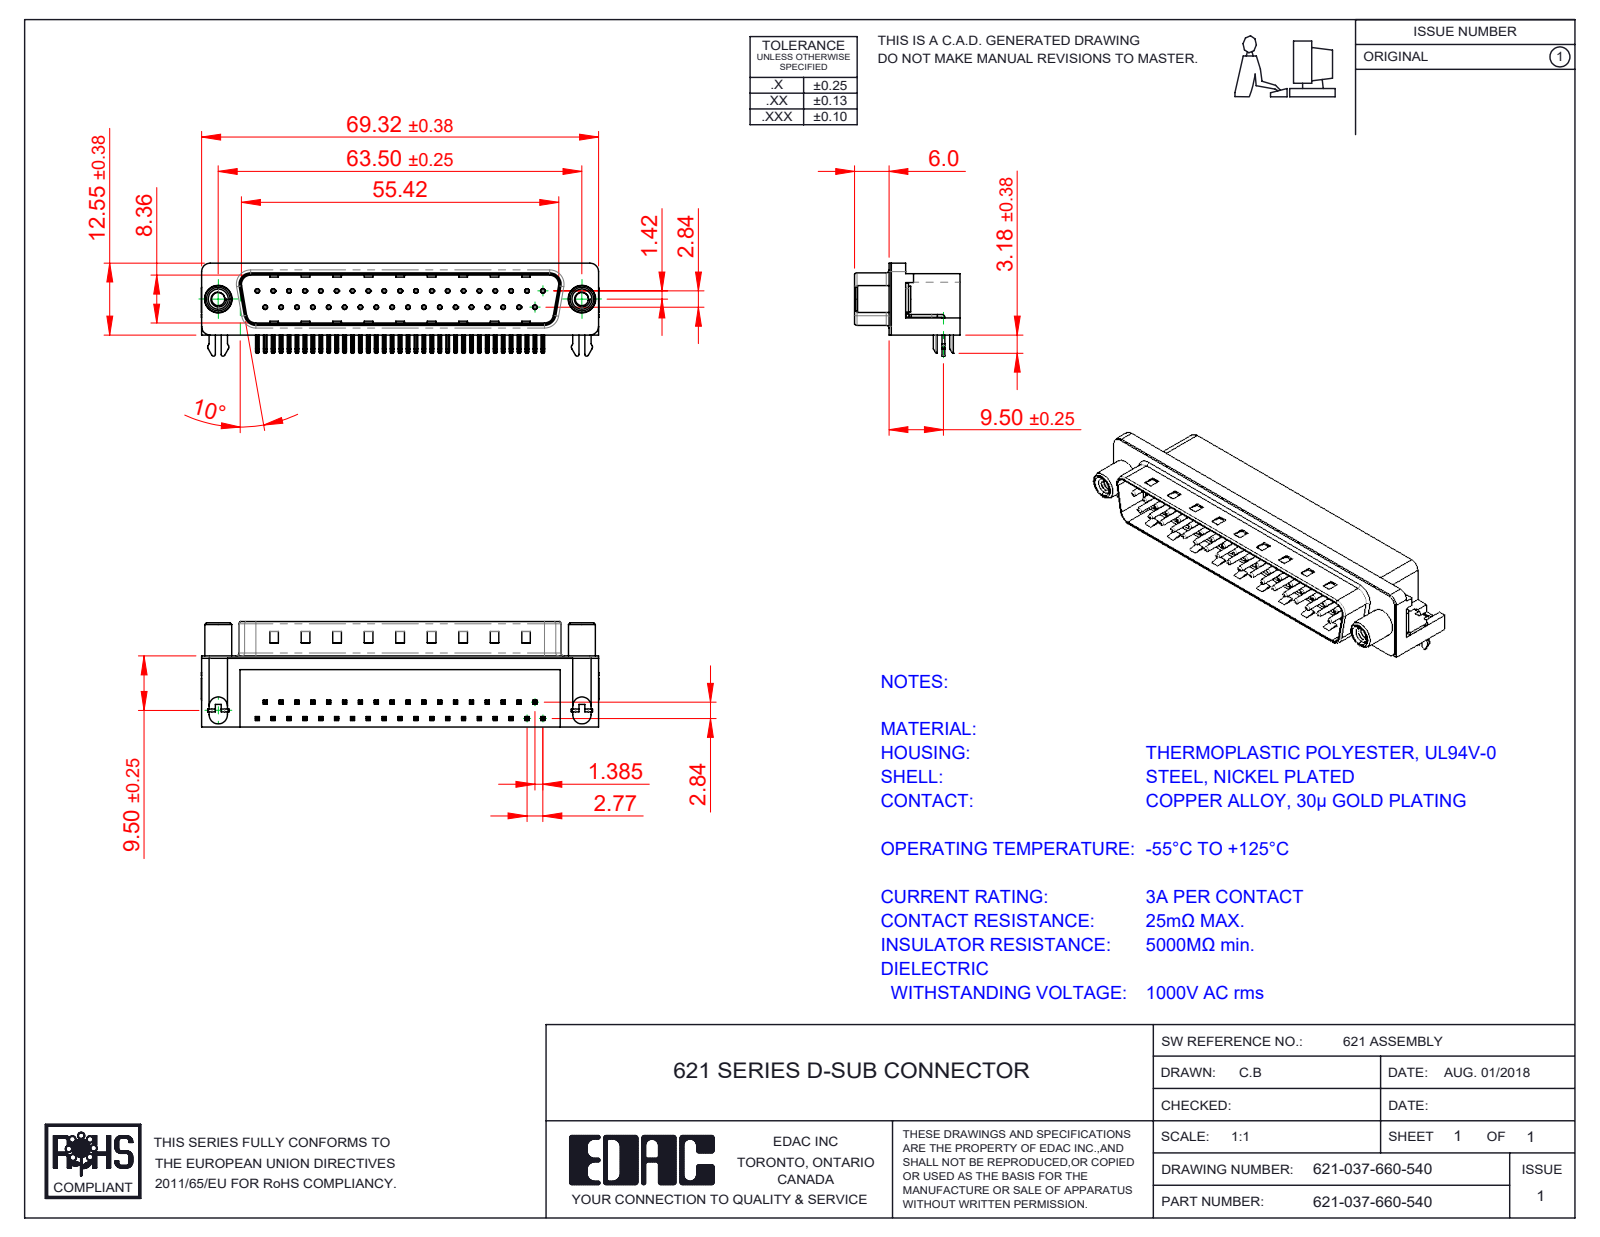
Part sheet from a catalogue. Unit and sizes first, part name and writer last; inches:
Units: inches
Overall size (bounding box): 2.732 × 0.724 × 0.64
Round holes (diameter × count): ⌀0.014 ×37, ⌀0.031 ×37, ⌀0.079 ×2, ⌀0.091 ×2, ⌀0.122 ×2, ⌀0.157 ×2, ⌀0.189 ×2, ⌀0.197 ×2
Round bosses / shafts (diameter × count): ⌀0.03 ×37, ⌀0.193 ×2, ⌀0.185 ×2, ⌀0.177 ×2, ⌀0.152 ×2, ⌀0.118 ×2
Partial cylindrical surfaces — rounded edges, fillets, slot ends (radius × count): R0.01 ×152, R0.005 ×74, R0.039 ×16, R0.02 ×9, R0.063 ×8, R0.059 ×7, R0.035 ×4, R0.079 ×4
Main face-to-face distances: 0.016, 0.472, 0.407, 0.345, 0.083, 0.067, 0.412, 0.428, 0.354, 0.488
Hole centre spacings: 0.124, 0.109, 0.218, 0.327, 0.436, 0.545, 0.763, 0.872
Volume: 0.532 in³ · Surface area: 16.07 in²
Bodies: 43 solids, 3313 faces (2047 planar, 929 cylindrical, 337 other)
Part name (STEP PRODUCT): 621 Housing_37 Socket; 621 Contact Bottom; 621 Contact Top; 621-037-660-540 (+3 more)
STEP written by: SolidWorks 2016 (CONFIG_CONTROL_DESIGN)
